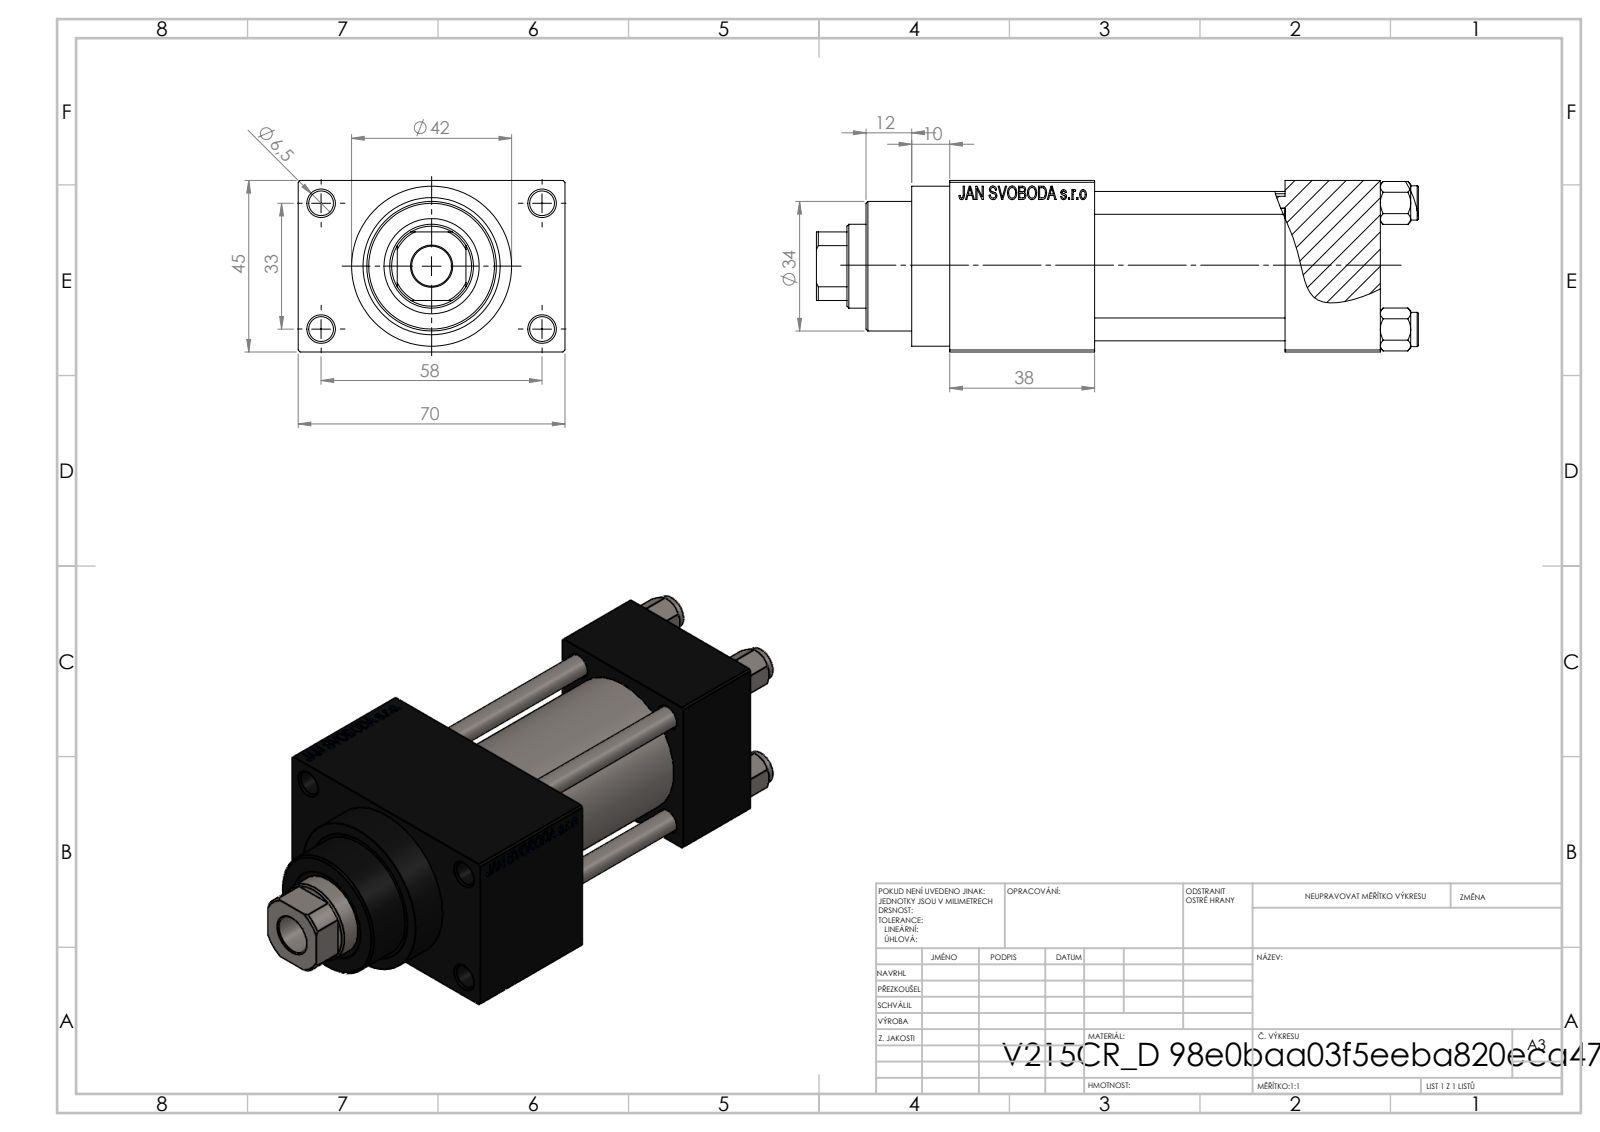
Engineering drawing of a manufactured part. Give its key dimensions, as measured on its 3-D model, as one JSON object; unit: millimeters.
{"part_name": "V215CR_D_Body; NUT_M5_D; V215CR_D_TYCINKA; V215CR_VCP_D (+1 more)", "step_written_by": "SolidWorks 2019 (CONFIG_CONTROL_DESIGN)", "units": "millimeters", "bodies": {"solids": 11, "faces": 1104, "planar": 496, "cylindrical": 88, "other": 520}, "overall_size": [158, 70, 45], "volume_mm3": 242876, "surface_area_mm2": 79884, "round_holes": [[6, 4], [6.5, 4], [7, 2], [13.16, 2], [20, 2], [10.5, 1], [22, 1], [24, 1], [25, 1], [32, 1], [33, 1]], "round_bosses_or_shafts": [[9, 4], [42, 1], [38, 1], [34, 1]], "partial_cylinders_radius": [[10.5, 1]], "face_to_face_distances": [45, 25, 50, 12.5, 75, 57.5, 88, 38, 113, 70], "hole_center_spacings": [12.4, 23.48, 33.2, 33.37, 35.35, 45.6, 56.35, 33]}
